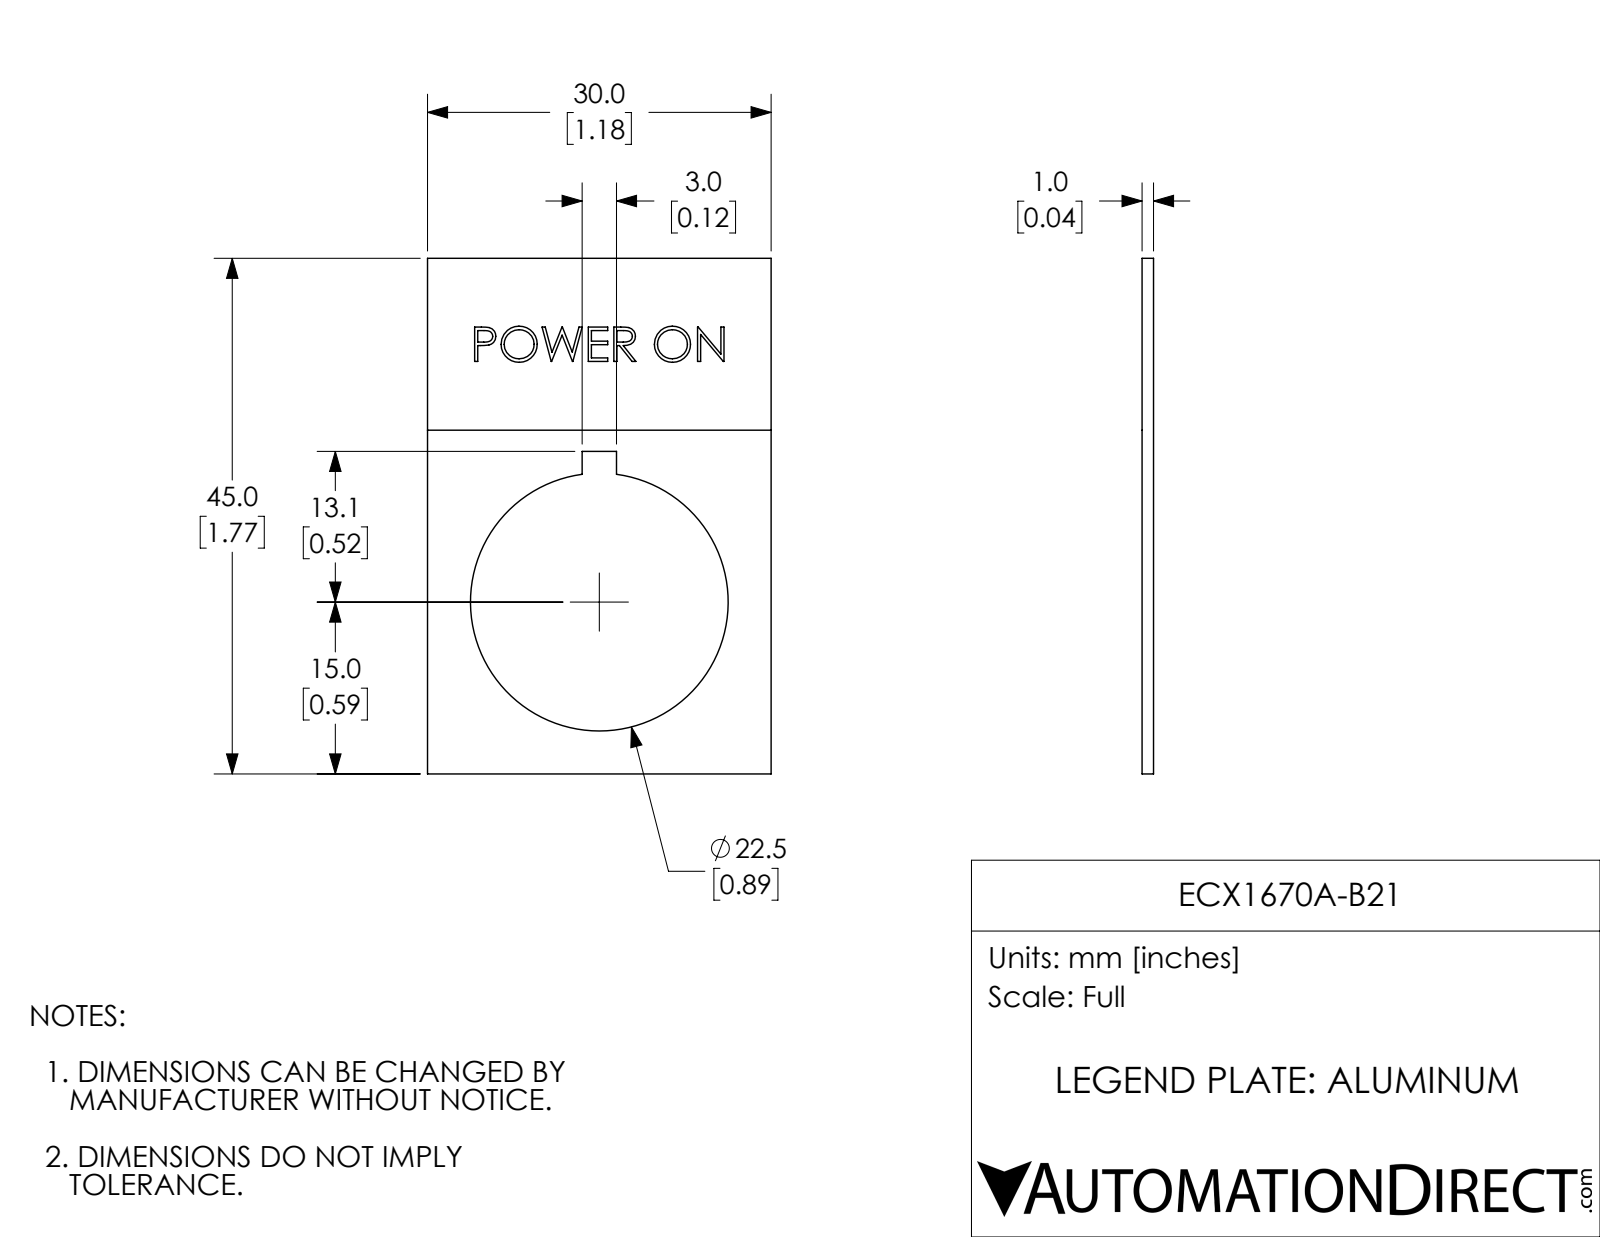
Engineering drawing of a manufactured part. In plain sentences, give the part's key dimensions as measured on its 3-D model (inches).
The part is named "ECX1670A-B21". Its 3-D file was written by "SolidWorks 2017 (AUTOMOTIVE_DESIGN)". It is 1 solid with 105 faces: 75 planar, 3 cylindrical and 27 other. Overall it measures 1.772 by 1.181 by 0.039 inches. Its volume is 0.058 cubic inches and its surface area 3.287 square inches. Round holes: 1 of diameter 0.886. The main face-to-face distances are 0.039, 1.181, 1.772, 0.038, 0.531, 0.65, 1.108, 0.663, 0.118, 0.088.
